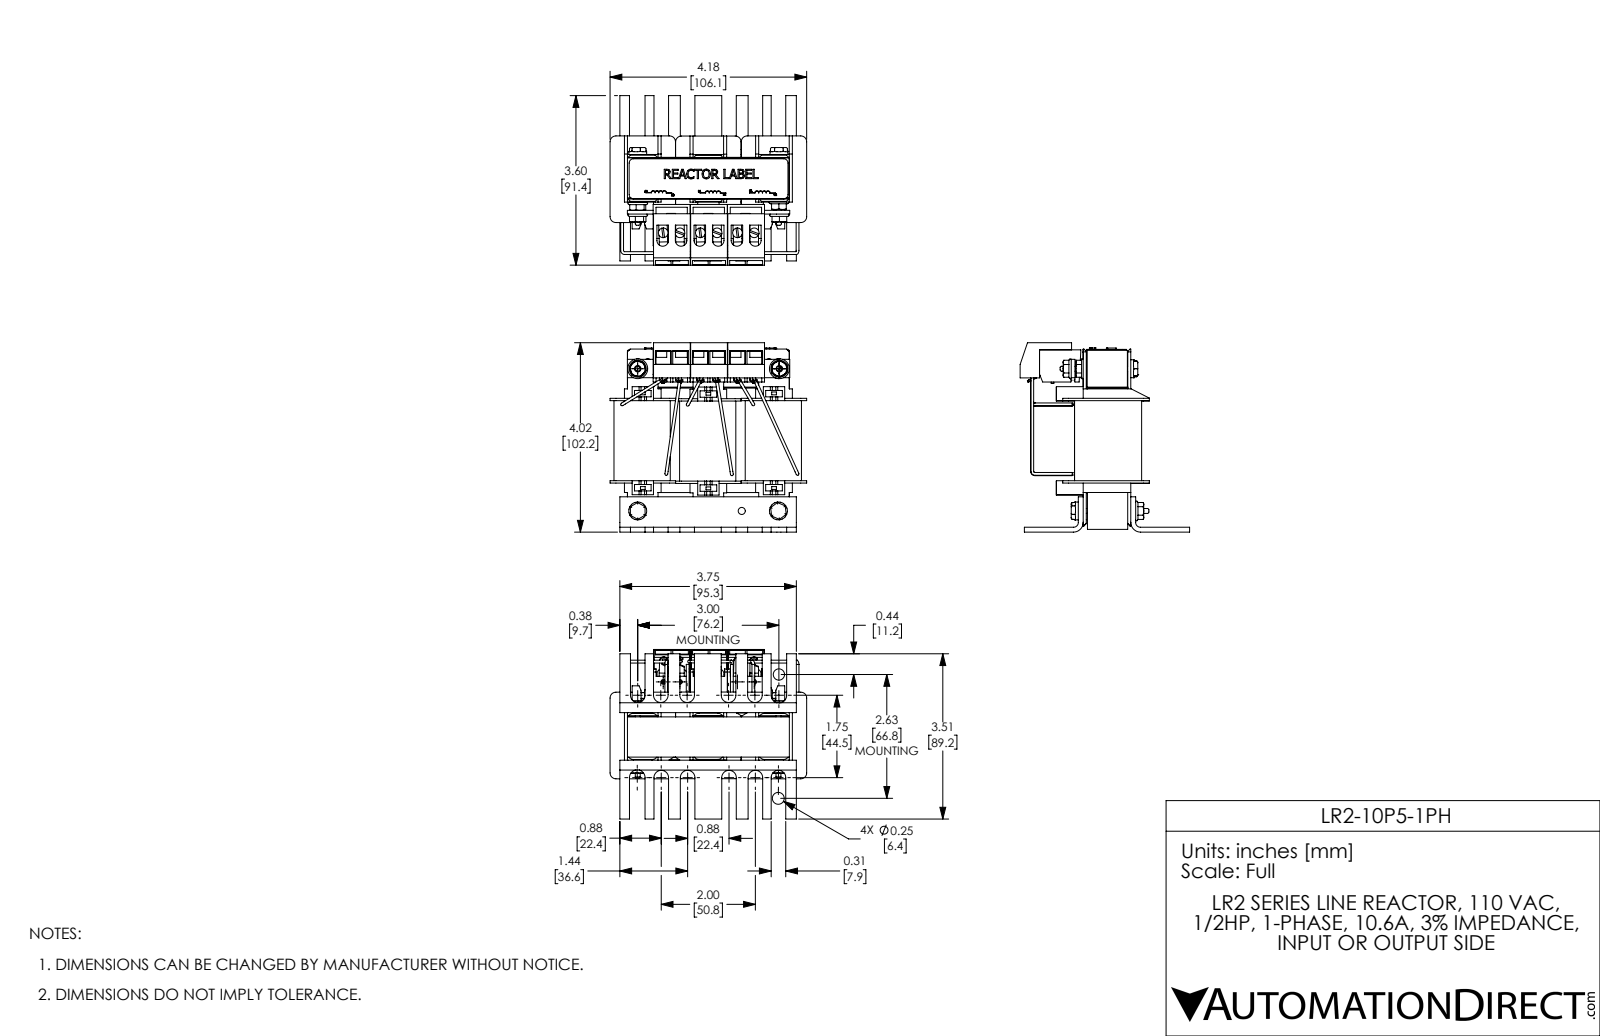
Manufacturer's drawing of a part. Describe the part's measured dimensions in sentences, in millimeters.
The part is named "A Frame Reactors Rep Reduction R2". Its 3-D file was written by "SolidWorks 2017 (AUTOMOTIVE_DESIGN)". It is 57 solids with 2039 faces: 1270 planar, 466 cylindrical and 303 other. Overall it measures 106.1 by 102.2 by 91.5 millimeters. Its volume is 223 700 cubic millimeters and its surface area 180 000 square millimeters. Round holes: 6 of diameter 2.5, 6 of diameter 3.6, 5 of diameter 2.6, 5 of diameter 4.9, 2 of diameter 1.9, 2 of diameter 3.8, 2 of diameter 4.8, 2 of diameter 5.5, 1 of diameter 1.9. Round bosses or shafts: 12 of diameter 1.5, 6 of diameter 1.4, 4 of diameter 9.7, 3 of diameter 5.2, 3 of diameter 5.2, 2 of diameter 1.2. Partial cylindrical surfaces (rounded edges, fillets, slot ends): 48 of radius 0.8, 18 of radius 3.2, 12 of radius 1, 12 of radius 1.2, 12 of radius 1.8, 12 of radius 5.2, 12 of radius 5.9, 10 of radius 3.9. The main face-to-face distances are 1.7, 35.4, 24, 18.2, 22.4, 70.8, 0.5, 21.9, 1.3, 44.5. The hole center spacings are 76.7, 20, 9, 76.9, 5.4, 11, 29.1, 35.4.
